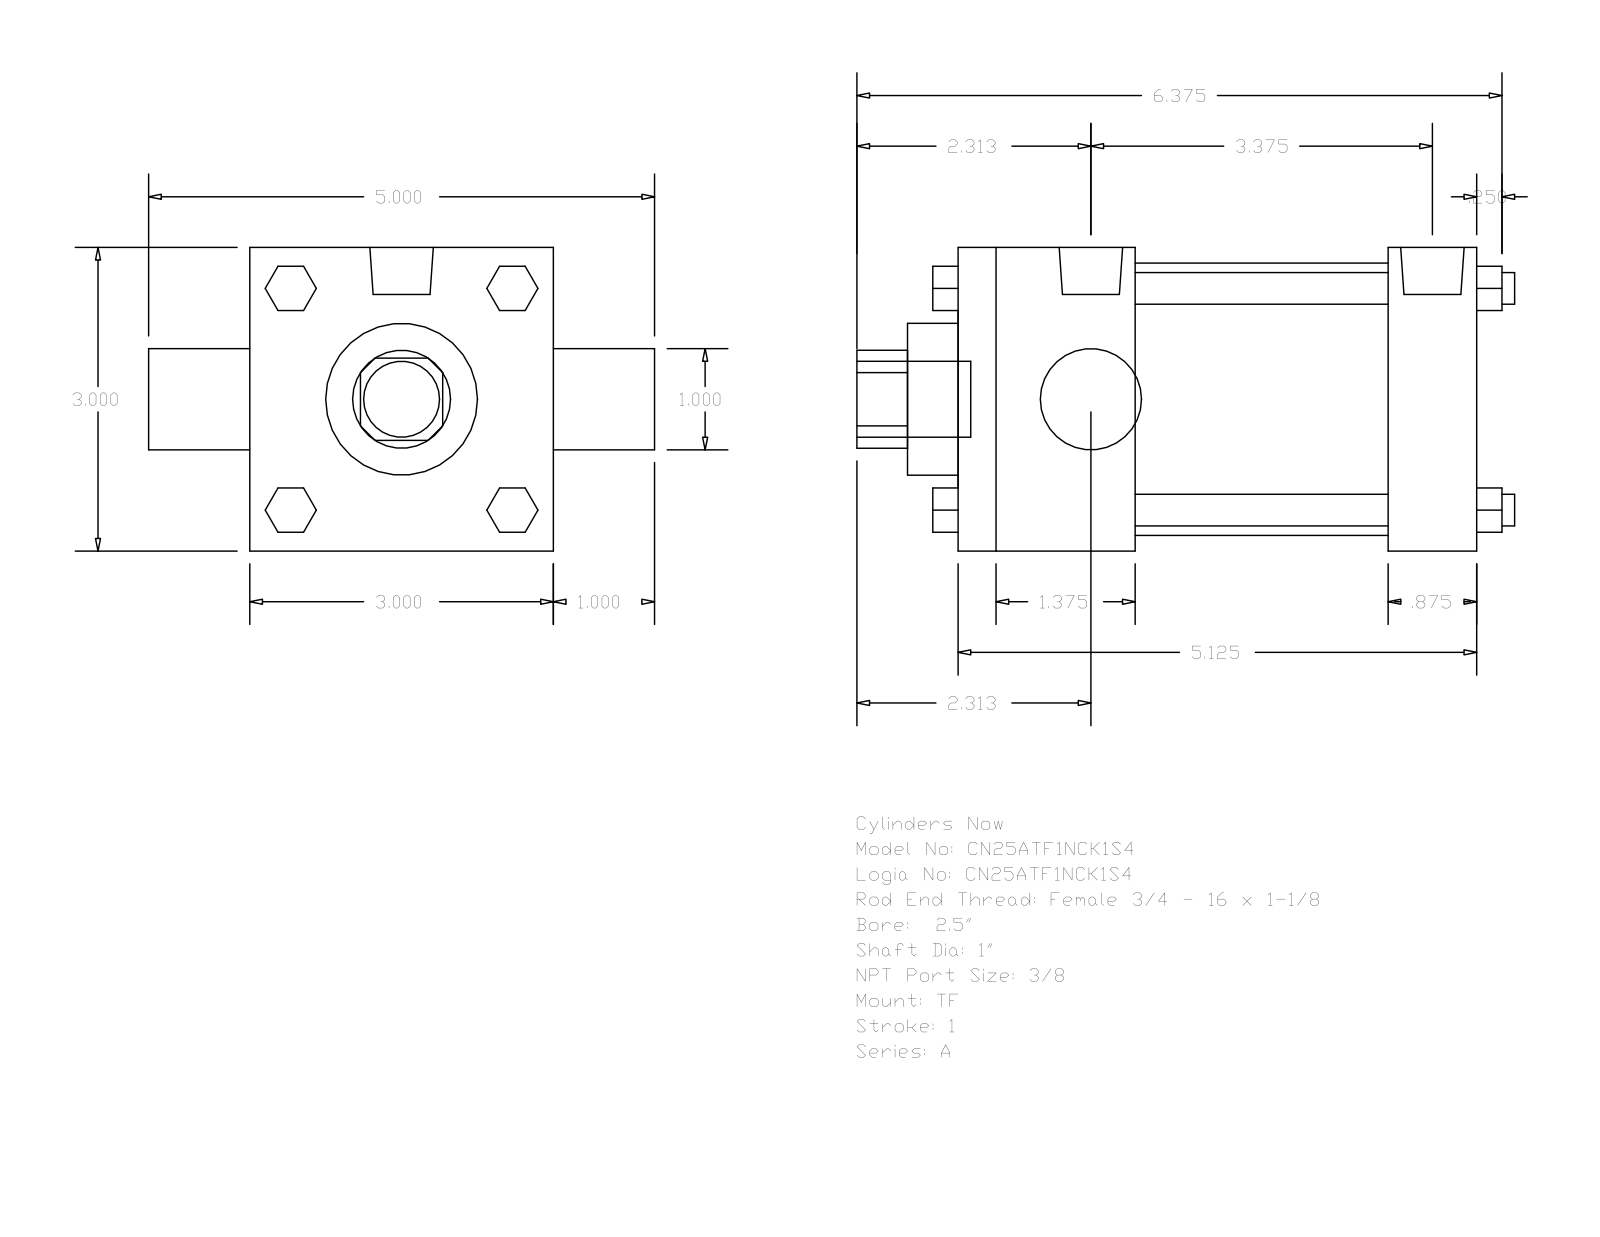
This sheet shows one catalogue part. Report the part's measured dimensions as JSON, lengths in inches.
{"part_name": "A_TF__0250_1", "step_written_by": "GSSL Pune (CONFIG_CONTROL_DESIGN)", "units": "inches", "bodies": {"solids": 0, "faces": 120, "planar": 92, "cylindrical": 28, "other": 0}, "overall_size": [6.5, 5, 3], "round_holes": [[1, 2], [1.5, 1], [2.69, 1]], "round_bosses_or_shafts": [[0.313, 4], [0.219, 3], [0.627, 2], [0.75, 1]], "partial_cylinders_radius": [[0.484, 1]], "face_to_face_distances": [3, 5.125, 1.75, 4.25, 2.5, 3.375, 0.875, 1, 4, 5]}
